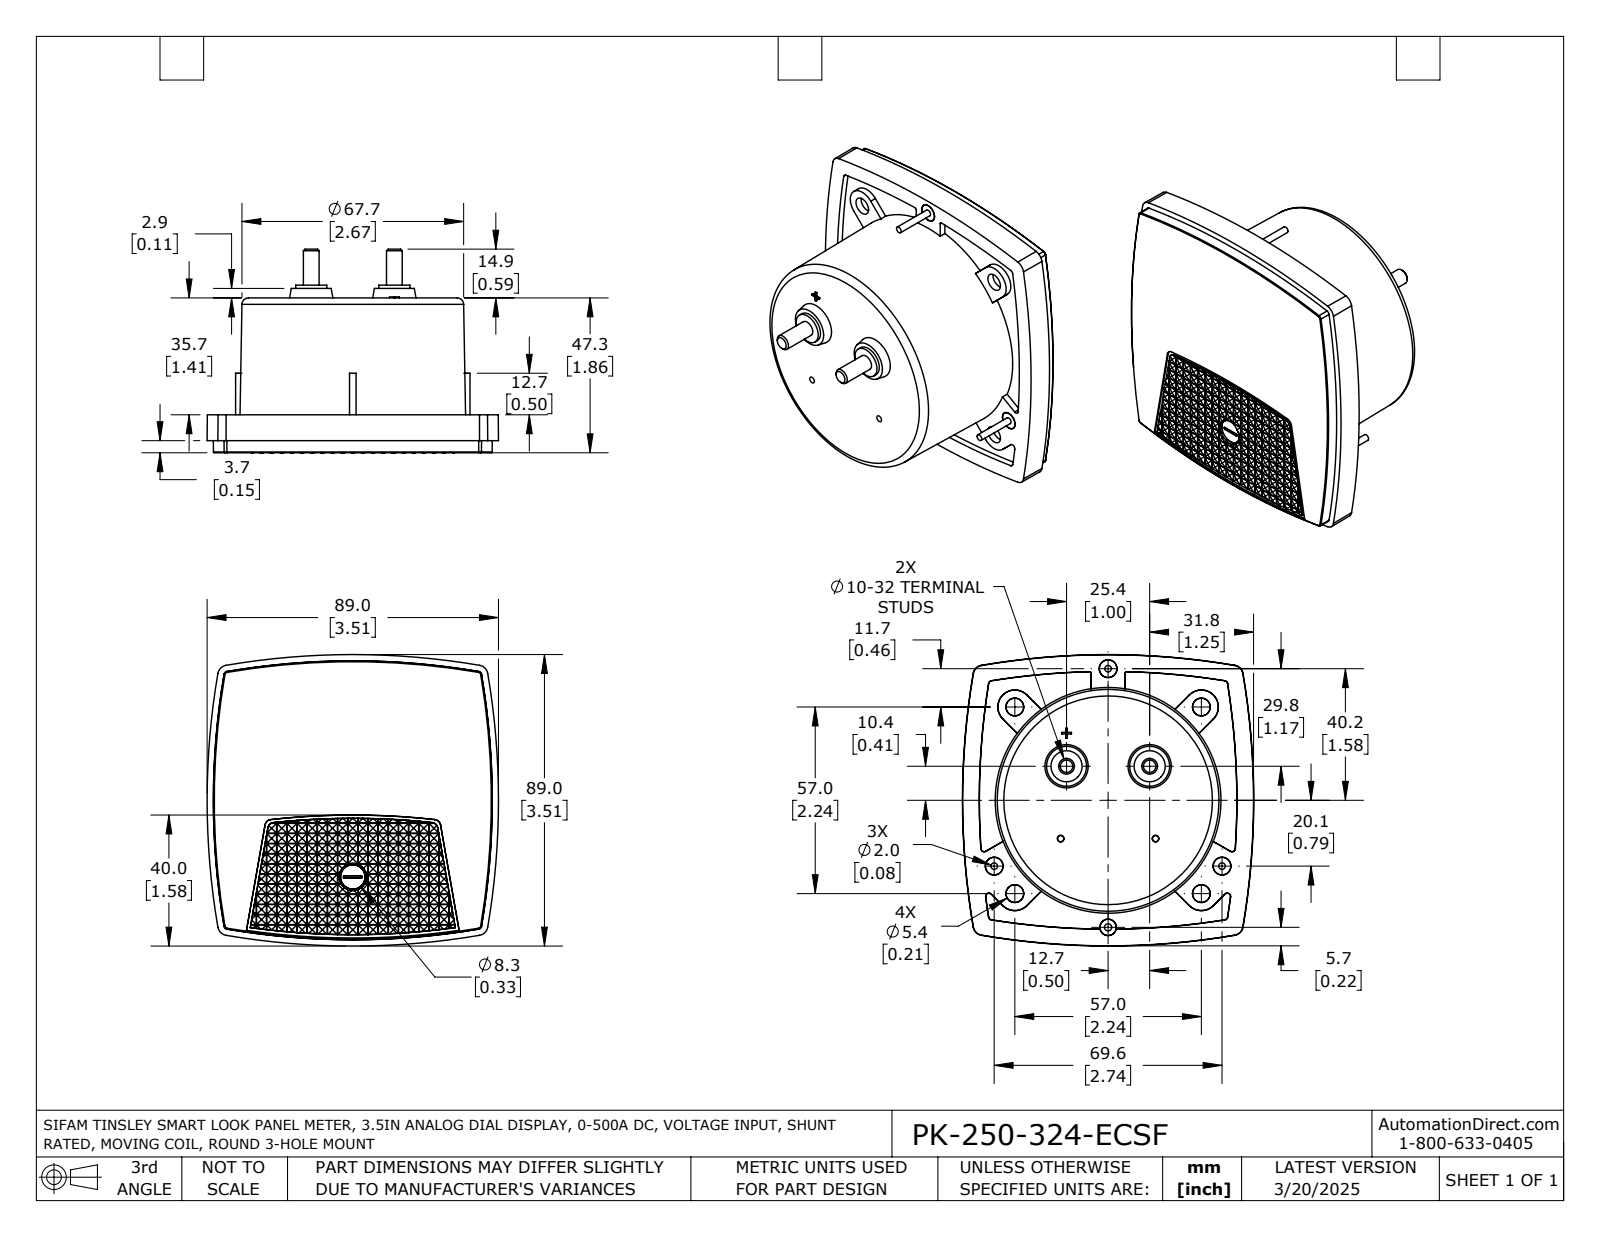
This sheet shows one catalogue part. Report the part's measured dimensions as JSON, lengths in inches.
{"part_name": "PK-250-324-ECSF", "step_written_by": "SolidWorks 2021 (AUTOMOTIVE_DESIGN)", "units": "inches", "bodies": {"solids": 1, "faces": 1078, "planar": 950, "cylindrical": 23, "other": 105}, "overall_size": [3.505, 3.505, 2.453], "volume_in3": 12.99, "surface_area_in2": 44.29, "round_holes": [[0.087, 1]], "round_bosses_or_shafts": [[0.213, 3], [0.079, 3], [0.374, 2], [0.189, 2]], "partial_cylinders_radius": [[8.961, 1]], "face_to_face_distances": [1.862, 1.406, 0.457, 0.079, 1.484, 0.378, 0.024, 0.096, 0.072, 0.12]}
